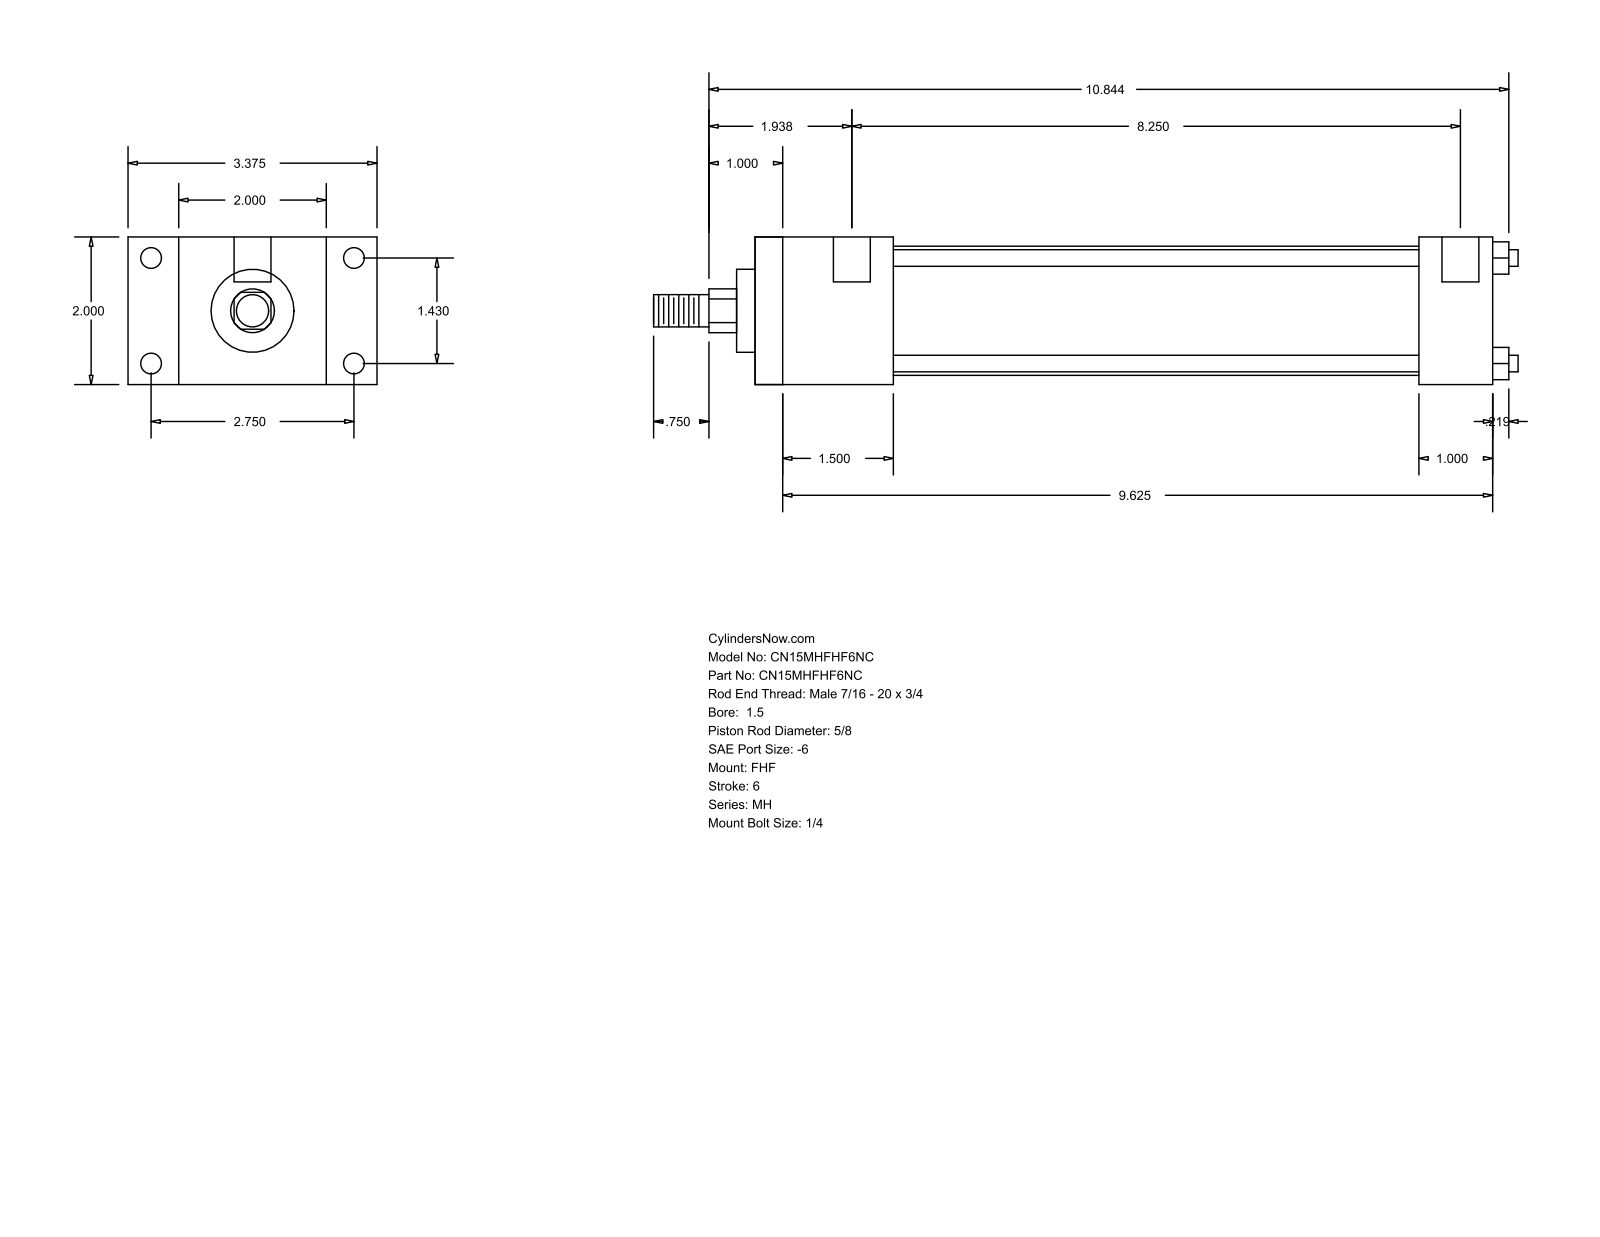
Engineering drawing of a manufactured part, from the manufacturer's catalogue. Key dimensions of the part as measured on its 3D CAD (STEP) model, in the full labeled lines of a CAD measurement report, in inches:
Part name (STEP PRODUCT): MH_FHF__0150_0.625
STEP written by: GSSL Pune (CONFIG_CONTROL_DESIGN)
Units: inches
Bodies: 0 solids, 88 faces (60 planar, 28 cylindrical, 0 other)
Overall size (bounding box): 11.719 × 3.375 × 2
Round holes (diameter × count): ⌀0.219 ×4, ⌀0.281 ×4, ⌀0.5 ×2
Round bosses / shafts (diameter × count): ⌀0.225 ×4, ⌀1.75 ×1, ⌀1.125 ×1, ⌀0.625 ×1, ⌀0.437 ×1
Partial cylindrical surfaces — rounded edges, fillets, slot ends (radius × count): R0.297 ×1
Main face-to-face distances: 2, 0.687, 2.687, 1.875, 3.375, 10, 8.125, 9, 7.125, 1
Hole centre spacings: 1.43, 2.75, 3.099, 8.375, 0.125, 8.25
